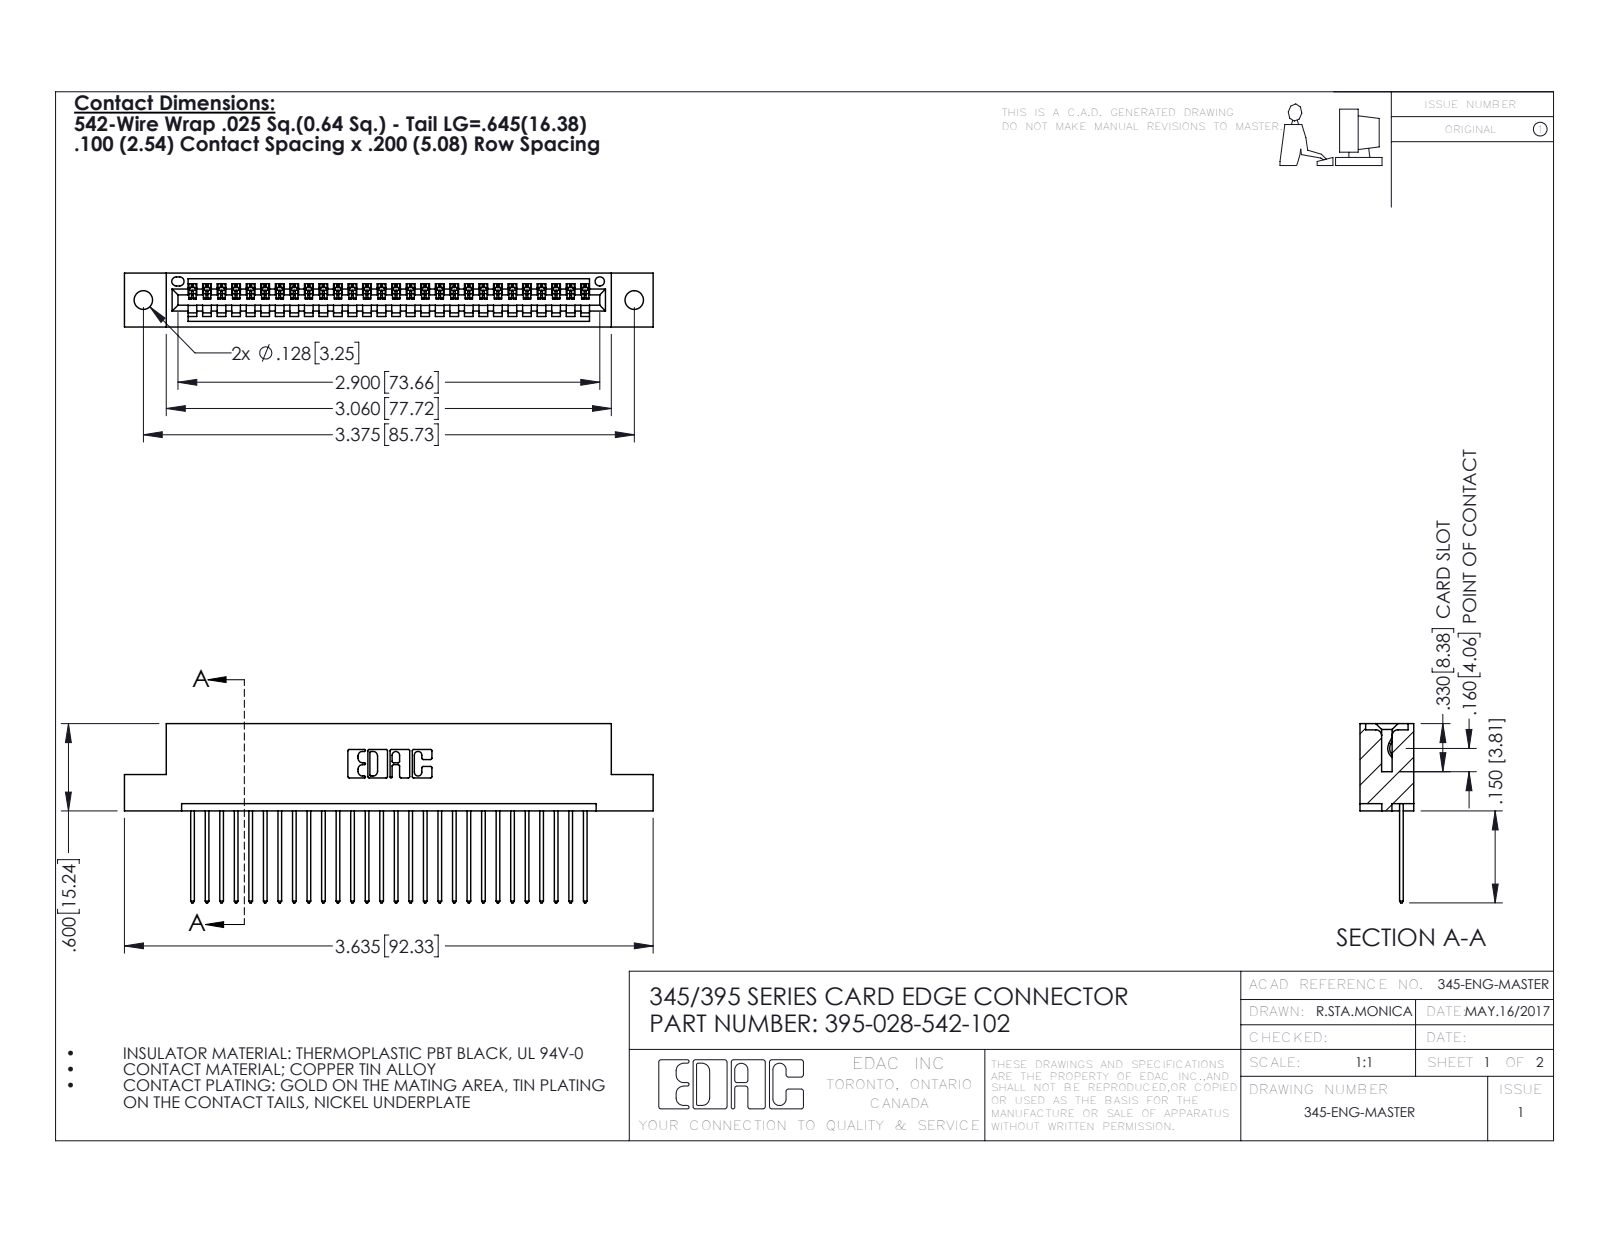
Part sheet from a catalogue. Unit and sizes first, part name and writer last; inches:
Units: inches
Overall size (bounding box): 3.635 × 1.232 × 0.37
Round holes (diameter × count): ⌀0.128 ×2, ⌀0.064 ×1
Partial cylindrical surfaces — rounded edges, fillets, slot ends (radius × count): R0.006 ×56, R0.01 ×56, R0.01 ×22, R0.007 ×6, R0.031 ×6, R0.026 ×3, R0.031 ×2, R0.04 ×2
Main face-to-face distances: 0.298, 0.072, 0.2, 0.37, 0.098, 0.272, 0.025, 0.225, 0.149, 0.072
Hole centre spacings: 0.27, 3.14, 3.375
Volume: 0.53 in³ · Surface area: 17.77 in²
Bodies: 29 solids, 1750 faces (1200 planar, 550 cylindrical, 0 other)
Part name (STEP PRODUCT): 395-028-542-102; 345 Part_Flush Mounting Lugs - 0.128 Dia; 345-292-001_345-293-142
STEP written by: SolidWorks 2016 (CONFIG_CONTROL_DESIGN)
